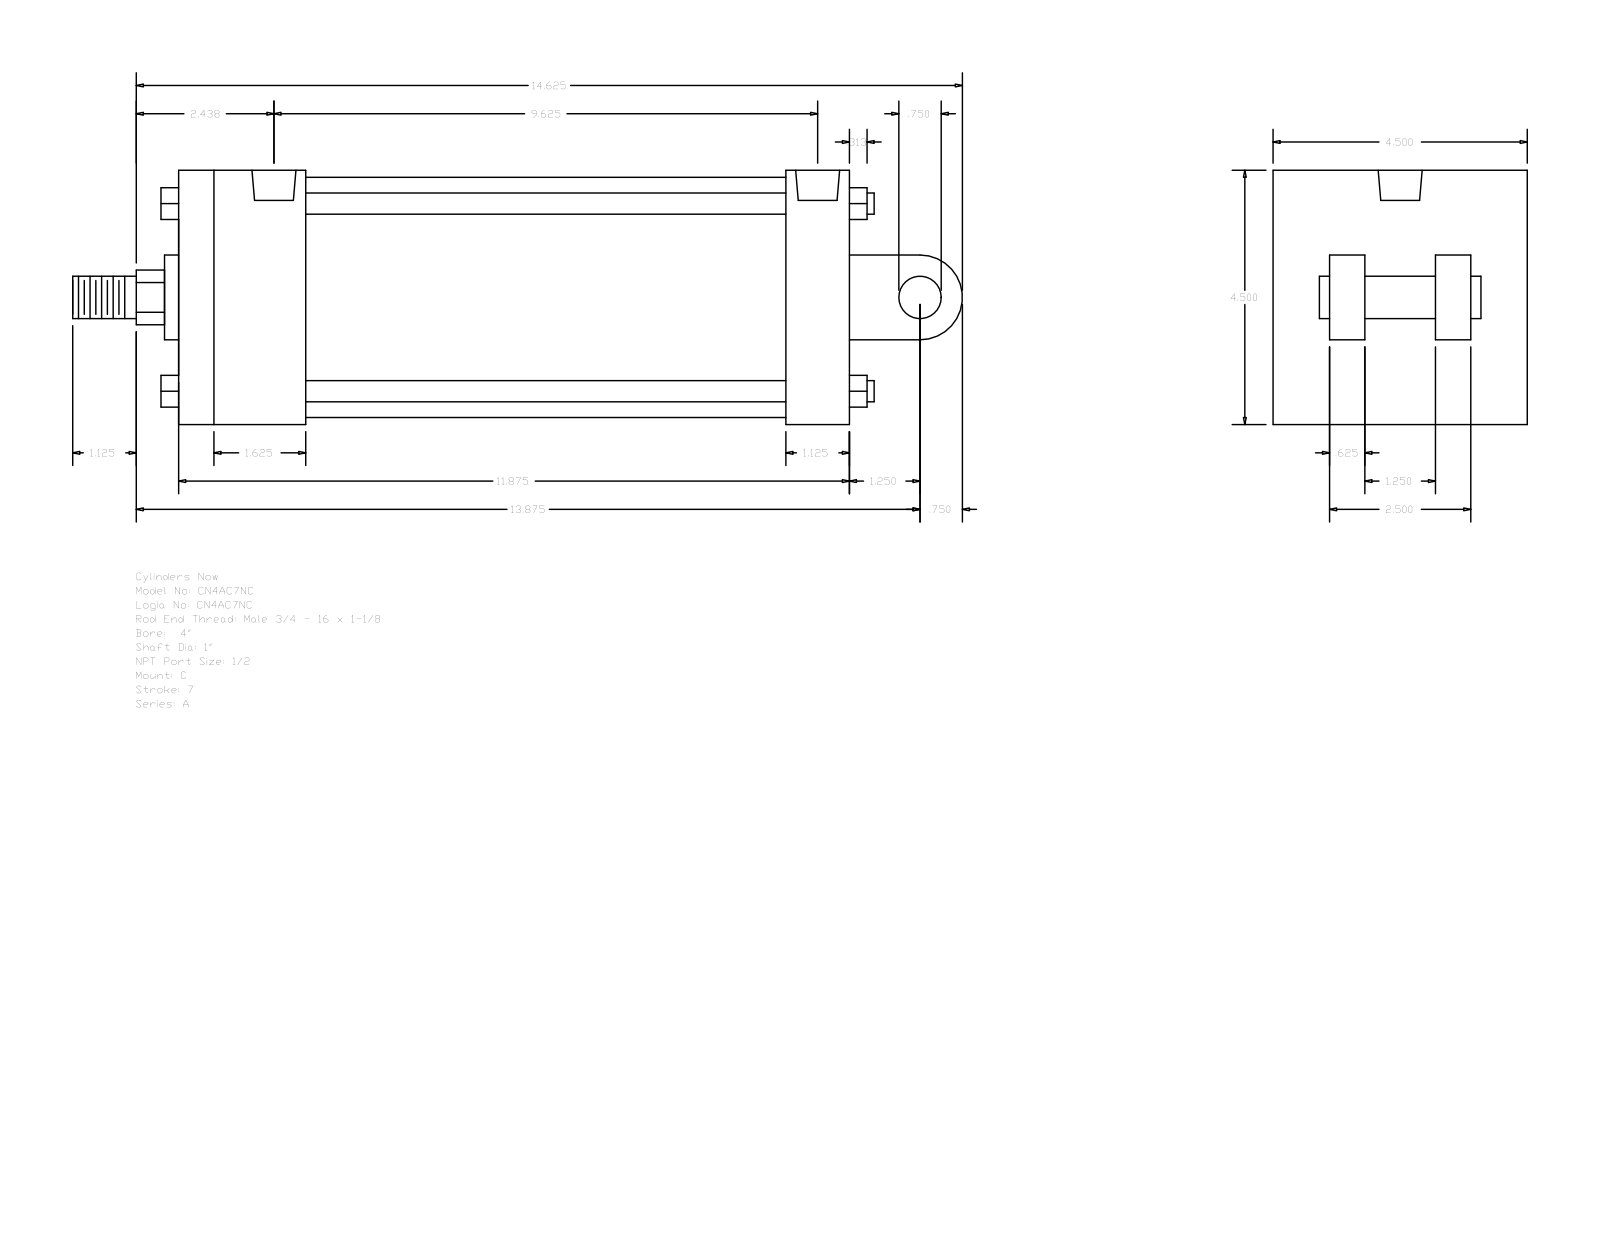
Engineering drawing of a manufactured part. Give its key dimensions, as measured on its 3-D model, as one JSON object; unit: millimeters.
{"part_name": "A_C__0400_1", "step_written_by": "GSSL Pune (CONFIG_CONTROL_DESIGN)", "units": "millimeters", "bodies": {"solids": 0, "faces": 135, "planar": 102, "cylindrical": 33, "other": 0}, "overall_size": [400.05, 114.3, 114.3], "round_holes": [[8.73, 4], [19.77, 2]], "round_bosses_or_shafts": [[9.53, 4], [19.05, 2], [107.95, 1], [38.1, 1], [25.4, 1]], "partial_cylinders_radius": [[12.29, 1], [19.05, 1]], "face_to_face_distances": [114.3, 301.63, 73.03, 273.05, 28.58, 57.15, 215.9, 244.48, 41.27, 38.1], "hole_center_spacings": [3.18, 238.12, 241.3, 244.48]}
